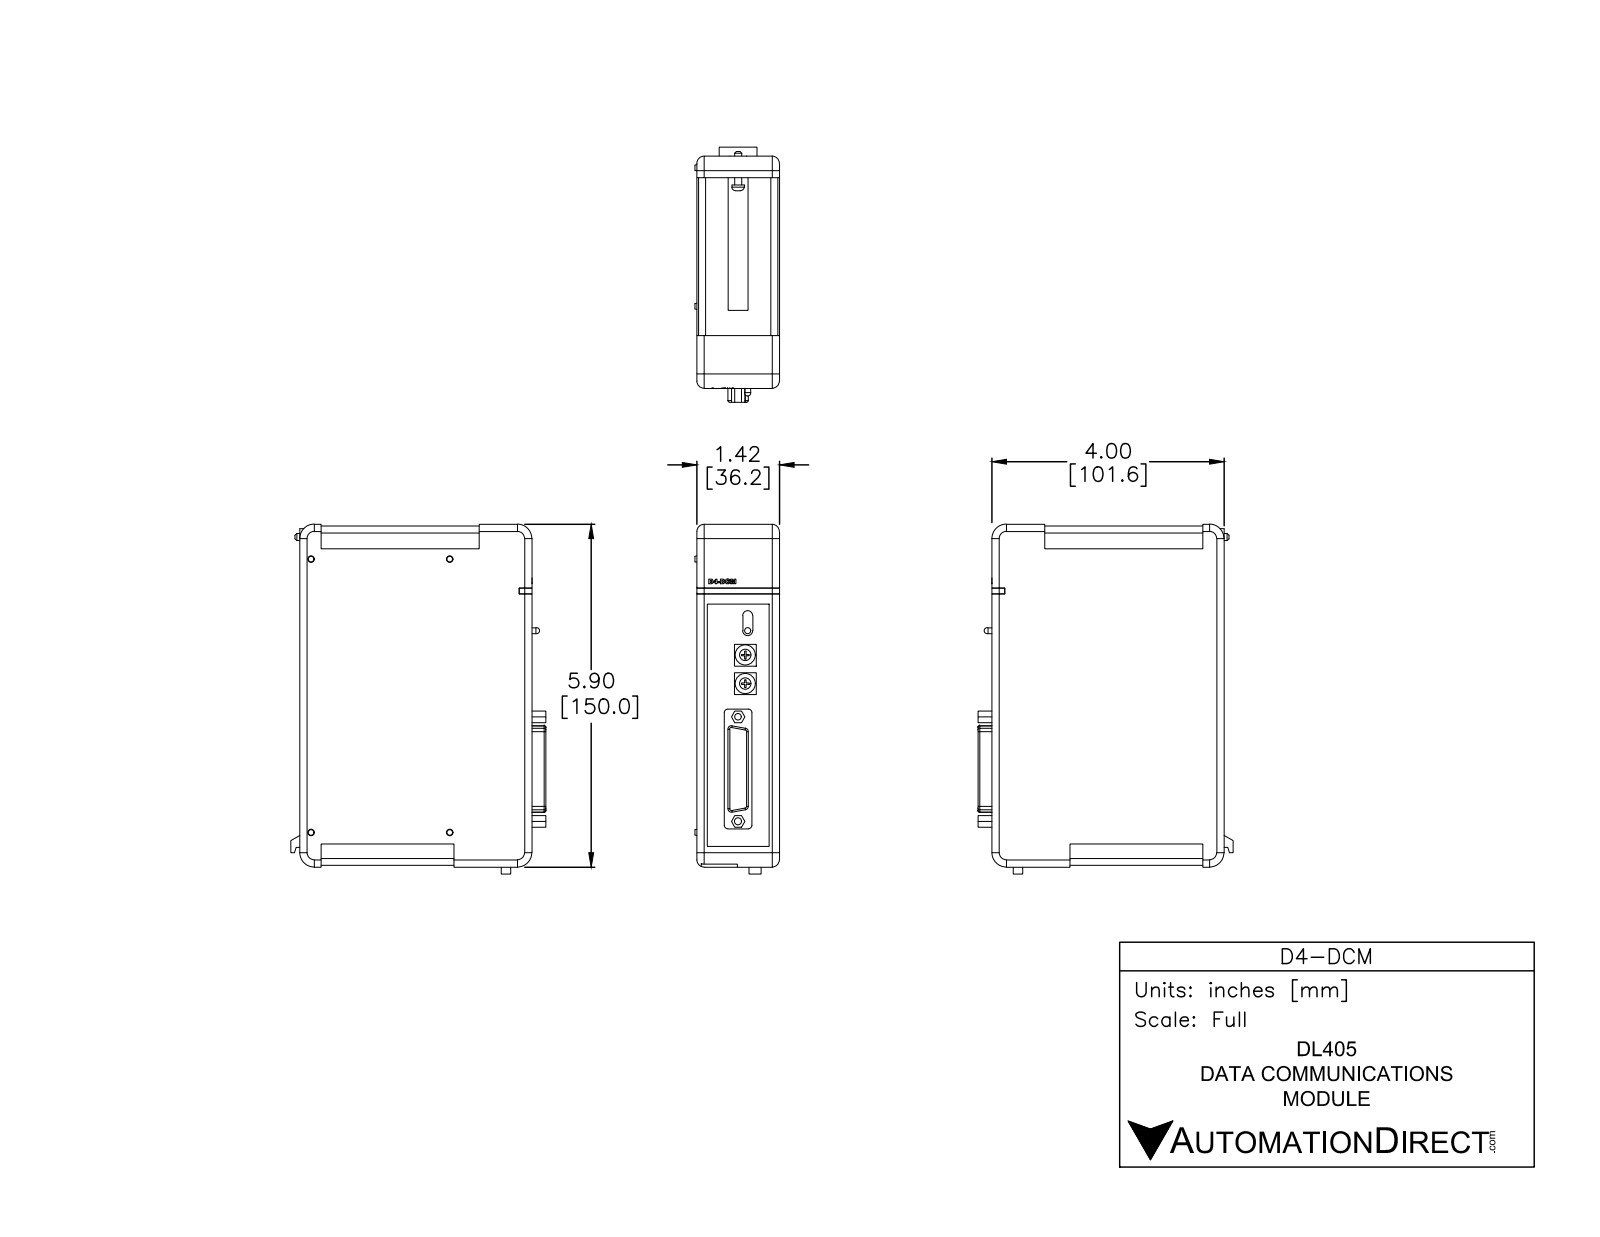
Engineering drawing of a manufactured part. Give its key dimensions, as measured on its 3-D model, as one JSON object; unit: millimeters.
{"part_name": "D4-DCM", "step_written_by": "SolidWorks 2014 (AUTOMOTIVE_DESIGN)", "units": "millimeters", "bodies": {"solids": 2, "faces": 330, "planar": 216, "cylindrical": 62, "other": 52}, "overall_size": [153, 111.6, 37], "volume_mm3": 529600, "surface_area_mm2": 53150, "round_holes": [[8.9, 2], [2.9, 1], [3.1, 1]], "round_bosses_or_shafts": [[5, 2], [5.4, 1], [3.1, 1], [2.5, 1]], "partial_cylinders_radius": [[1.5, 8], [3.2, 8], [0.8, 4], [3, 4], [6.4, 4], [2.2, 2], [3.7, 1], [4.3, 1]], "face_to_face_distances": [36.2, 0.8, 100.8, 35.4, 101.6, 148.5, 149.2, 5.1, 95.8, 96.5], "hole_center_spacings": [12.5, 14.8, 27.2, 45.7, 60.3, 72.7]}
